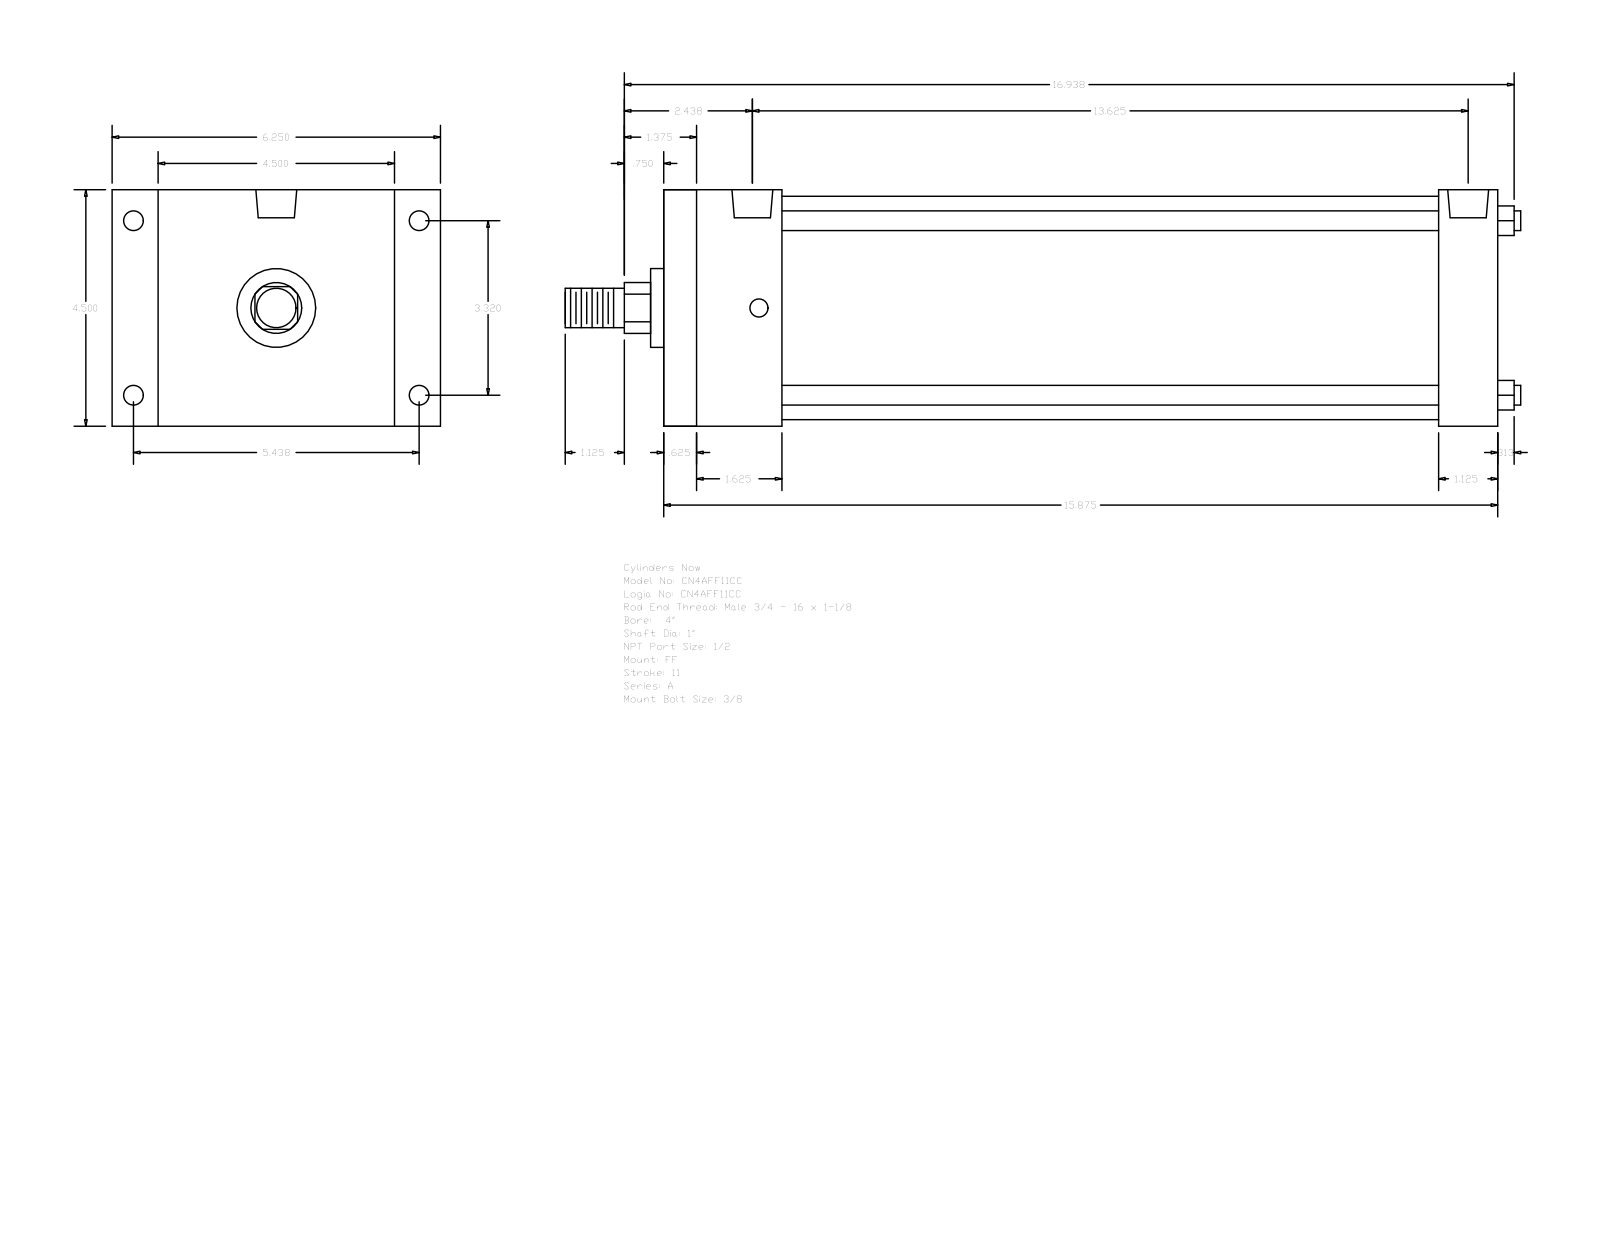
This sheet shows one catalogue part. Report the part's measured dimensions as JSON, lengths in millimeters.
{"part_name": "A_FF__0400_1", "step_written_by": "GSSL Pune (CONFIG_CONTROL_DESIGN)", "units": "millimeters", "bodies": {"solids": 0, "faces": 92, "planar": 64, "cylindrical": 28, "other": 0}, "overall_size": [461.96, 158.75, 114.3], "round_holes": [[8.73, 4], [9.53, 4], [19.77, 2]], "round_bosses_or_shafts": [[9.53, 4], [107.95, 1], [38.1, 1], [25.4, 1], [19.05, 1]], "partial_cylinders_radius": [[12.29, 1]], "face_to_face_distances": [114.3, 403.22, 15.87, 387.35, 28.57, 22.23, 136.53, 374.65, 358.78, 57.15], "hole_center_spacings": [3.18, 84.32, 138.12, 161.82, 339.72, 342.9, 346.08]}
